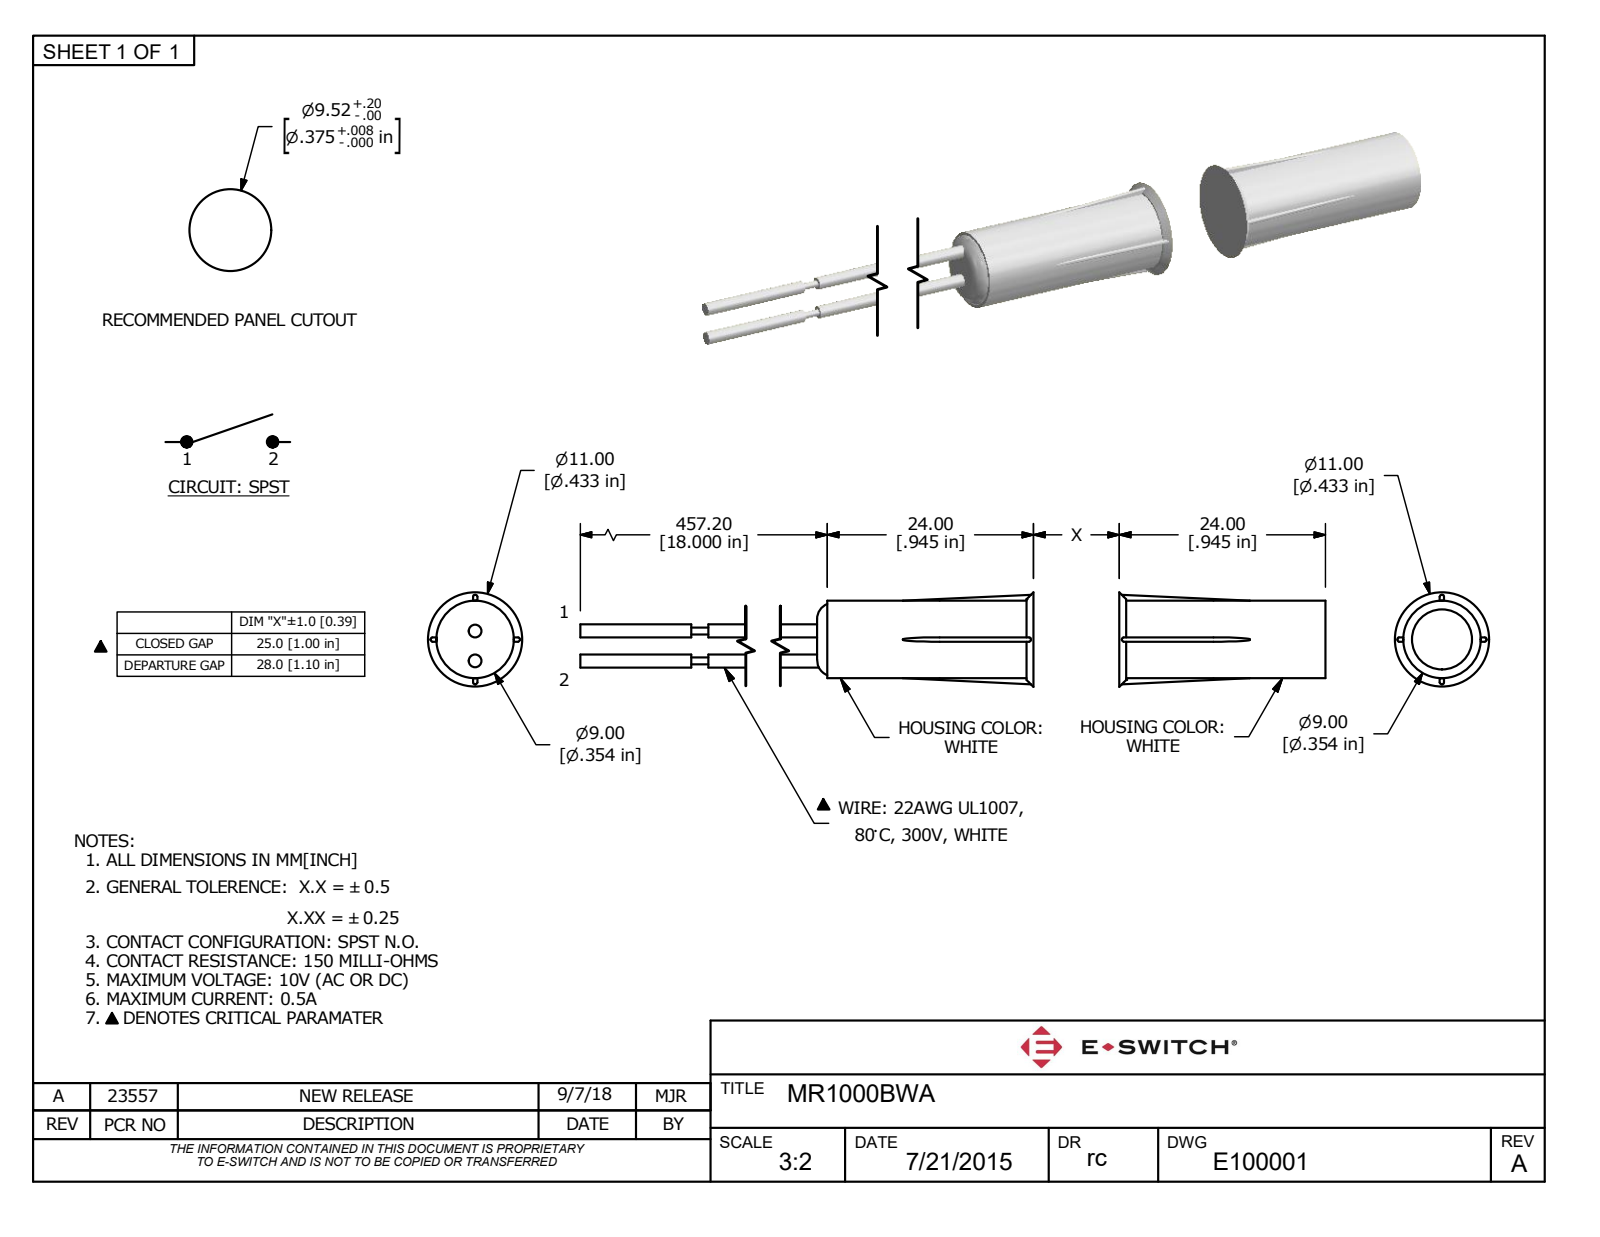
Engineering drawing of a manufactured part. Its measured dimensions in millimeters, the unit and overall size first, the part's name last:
Units: millimetres
Overall size (bounding box): 530.2 × 11 × 11
Round holes (diameter × count): ⌀7 ×1
Round bosses / shafts (diameter × count): ⌀1.5 ×2, ⌀0.8 ×2, ⌀9 ×1
Partial cylindrical surfaces — rounded edges, fillets, slot ends (radius × count): R0.2 ×16
Main face-to-face distances: 25, 4.25, 4.75, 24, 49, 9, 0.5, 25.2, 50.2, 74.2
Volume: 4 642 mm³ · Surface area: 6 248 mm²
Bodies: 2 solids, 122 faces (91 planar, 27 cylindrical, 4 other)
Part name (STEP PRODUCT): MR1000BWA
STEP written by: Autodesk Inventor 2018 (AP242_MANAGED_MODEL_BASED_3D_ENGINEERING_MIM_LF)
